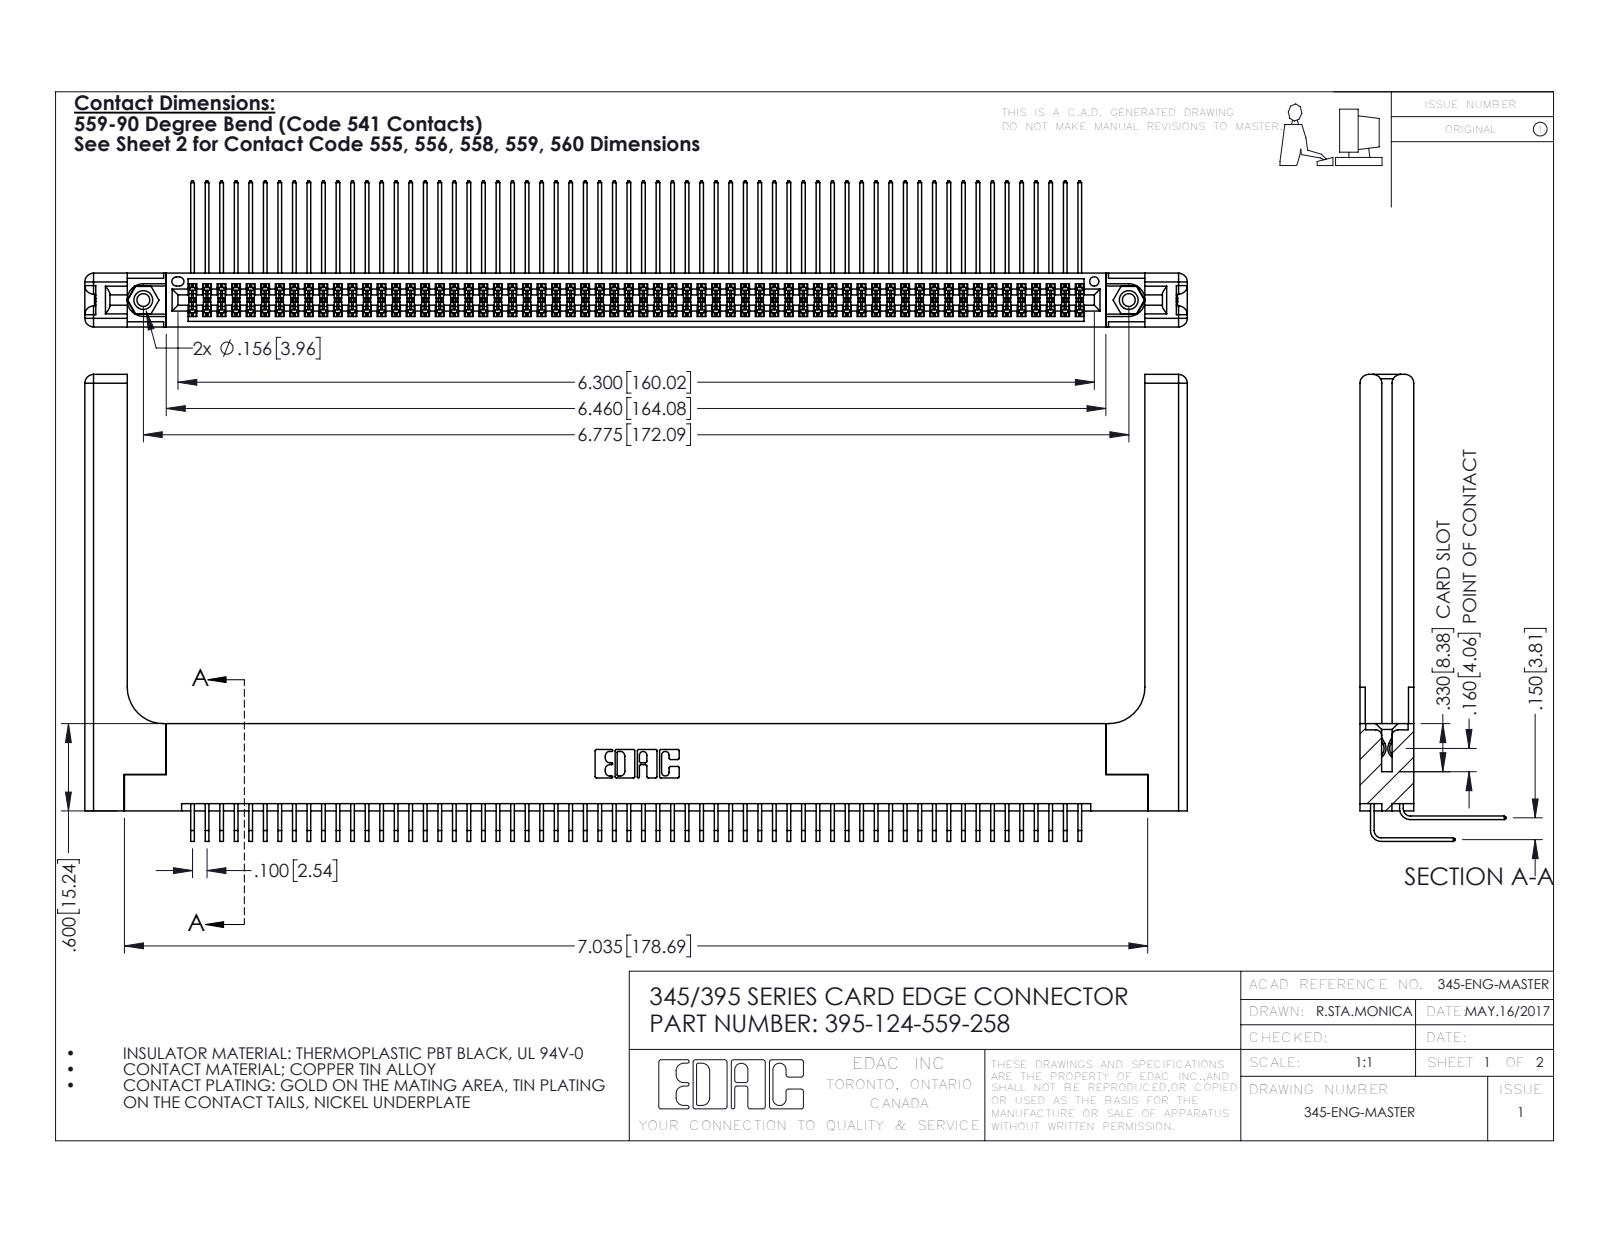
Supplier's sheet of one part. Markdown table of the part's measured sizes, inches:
| quantity | value |
| --- | --- |
| part name | 345-250-001_345-250-001-102; 345 Part_Flush Mounting Lugs - 0.156 Dia-TH; 395-124-559-258; 345-220-058_345-220-058 (+2 more) |
| STEP written by | SolidWorks 2016 (CONFIG_CONTROL_DESIGN) |
| units | inches |
| bodies | 129 solids, 6830 faces (4568 planar, 2202 cylindrical, 60 other) |
| overall size | 7.579 × 3.209 × 1.005 |
| volume | 1.713 in³ |
| surface area | 58.57 in² |
| round holes (diameter × count) | 0.089 × 2, 0.125 × 2, 0.156 × 2, 0.064 × 1 |
| round bosses / shafts (diameter × count) | 0.155 × 2 |
| partial cylindrical surfaces (radius × count) | 0.006 × 186, 0.01 × 22, 0.06 × 16, 0.007 × 6, 0.031 × 6, 0.026 × 3, 0.014 × 2, 0.019 × 2 |
| main face-to-face distances | 0.072, 0.298, 0.37, 0.2, 0.098, 0.272, 0.025, 0.225, 0.175, 0.15 |
| hole center spacings | 0.27, 6.539, 6.775 |
